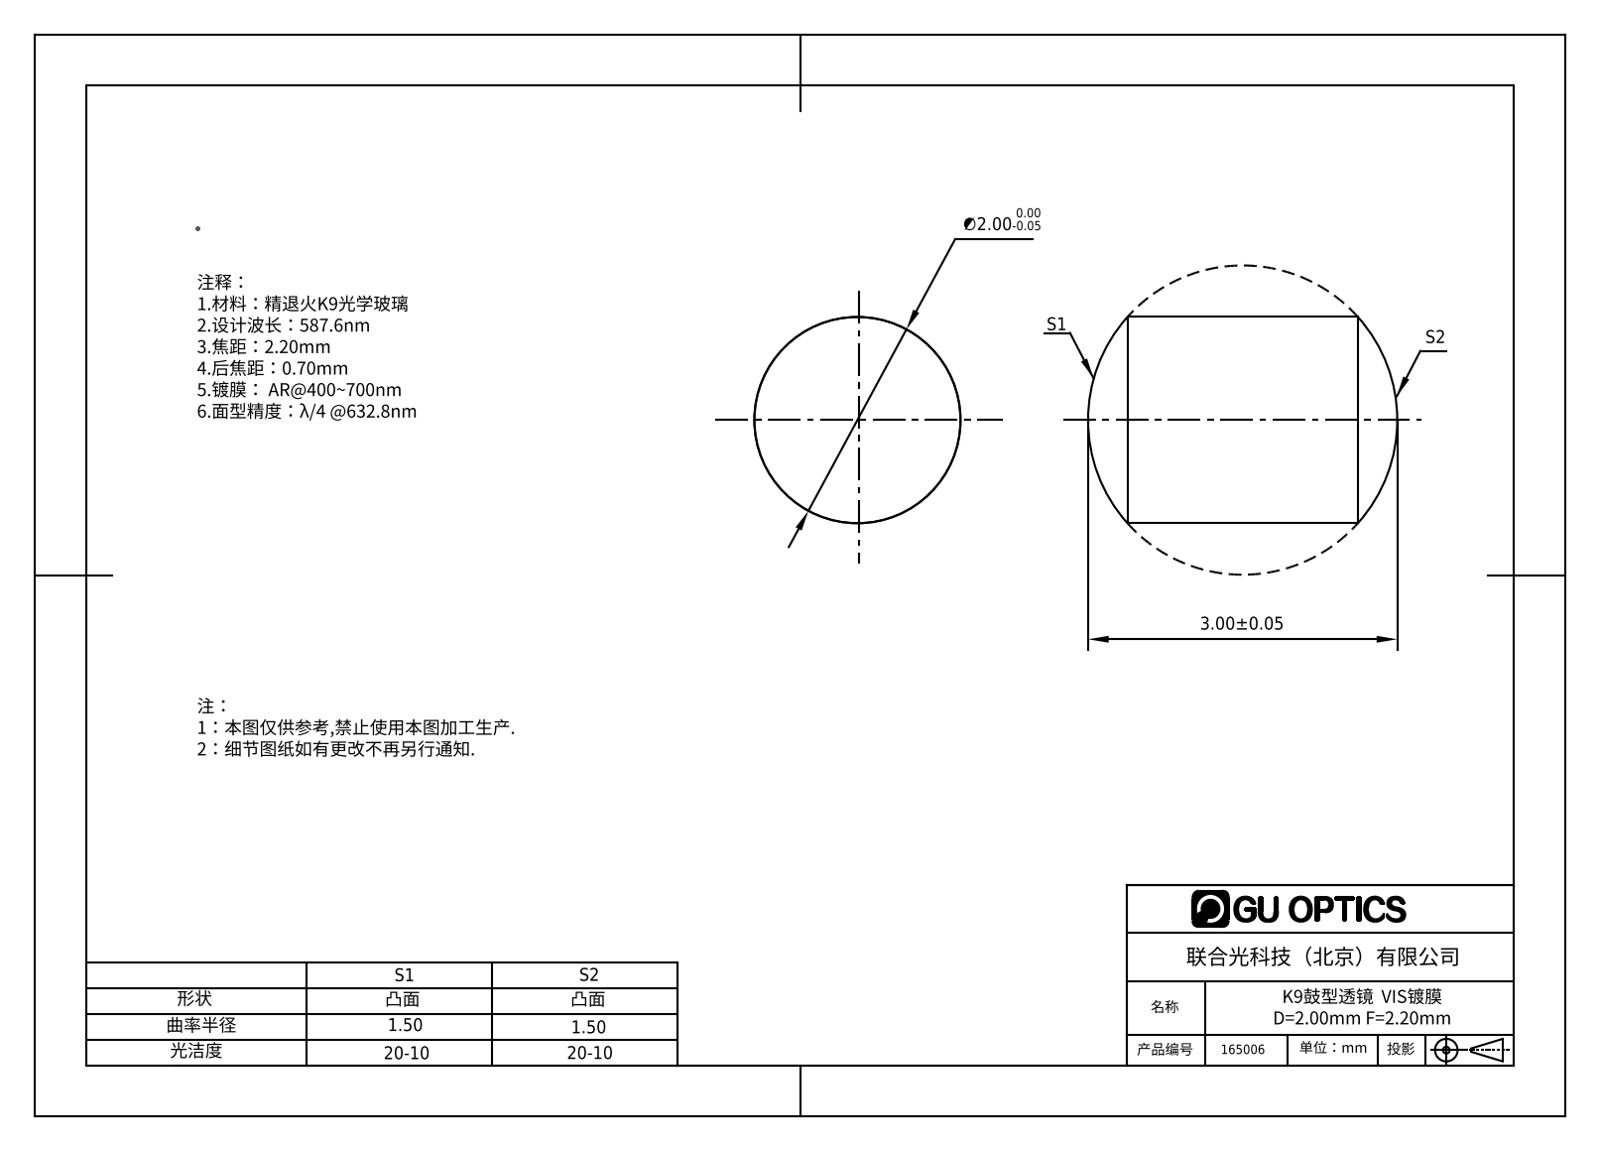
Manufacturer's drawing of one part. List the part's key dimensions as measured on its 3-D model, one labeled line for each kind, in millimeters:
Part name (STEP PRODUCT): 165001
STEP written by: SolidWorks 2016 (CONFIG_CONTROL_DESIGN)
Units: millimetres
Bodies: 1 solid, 6 faces (0 planar, 2 cylindrical, 4 other)
Overall size (bounding box): 3 × 2 × 2
Volume: 8 mm³ · Surface area: 21 mm²
Round bosses / shafts (diameter × count): ⌀2 ×1
